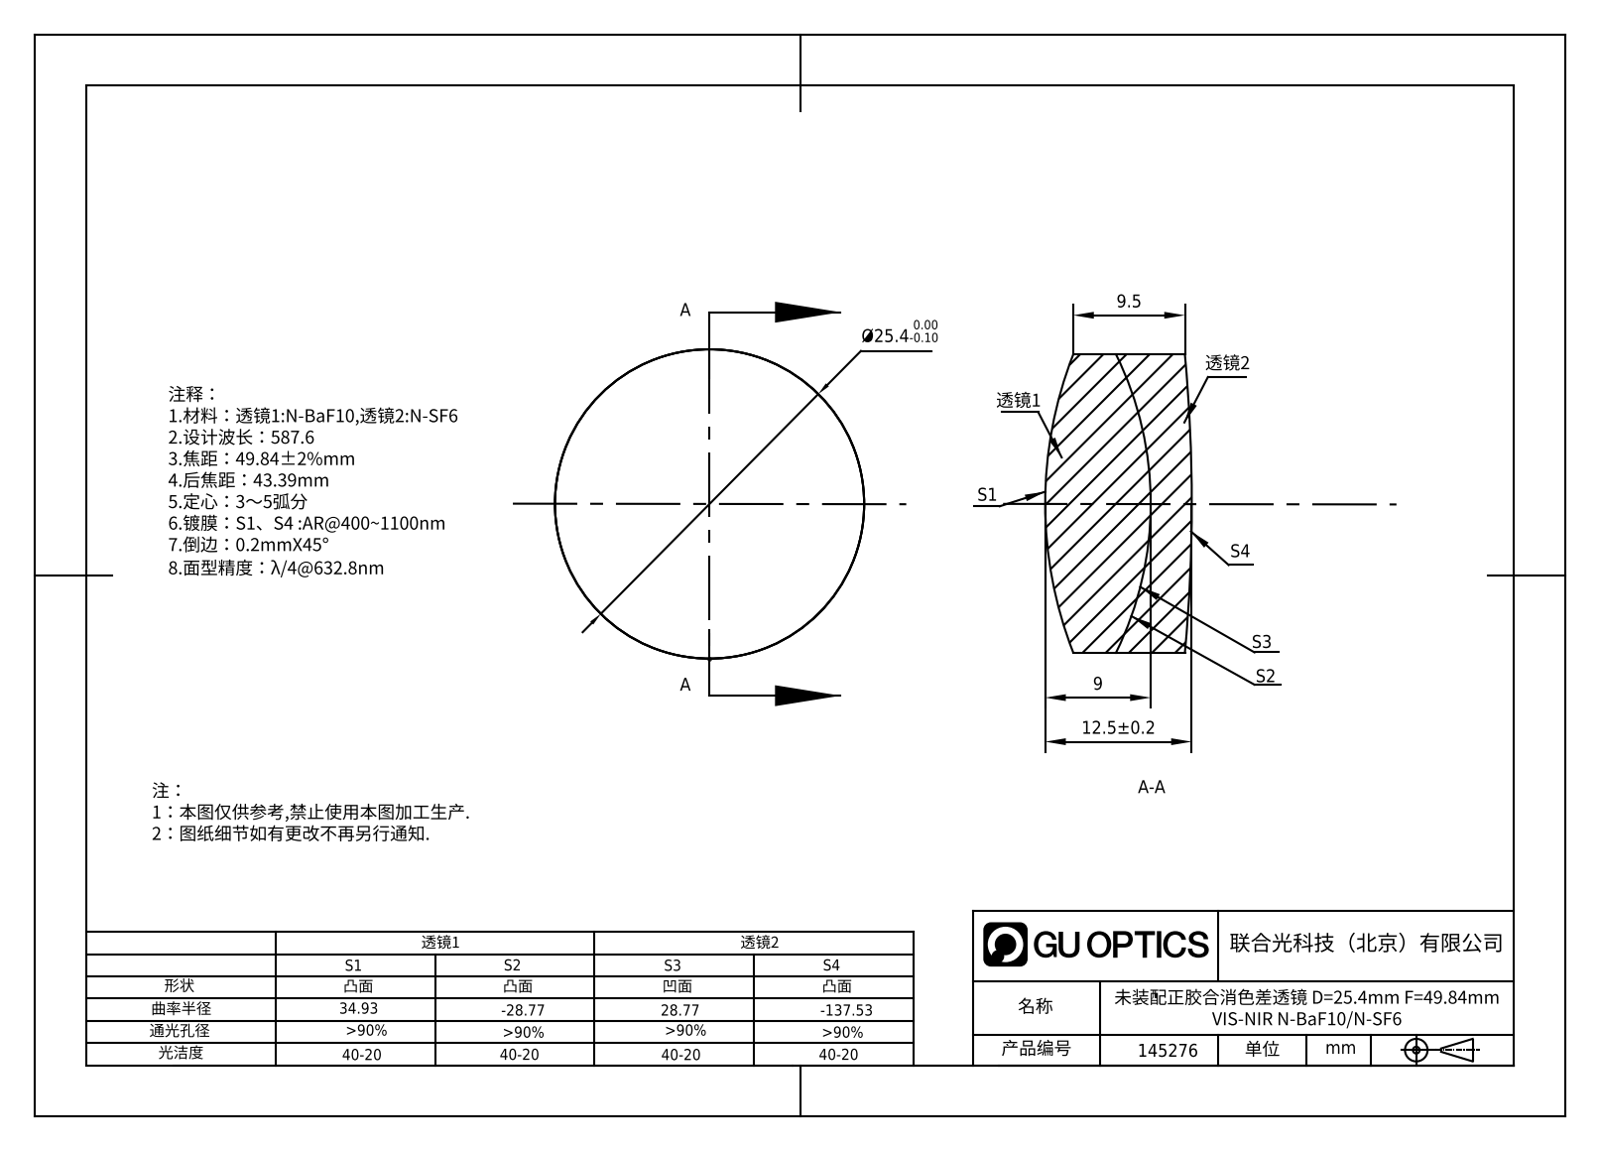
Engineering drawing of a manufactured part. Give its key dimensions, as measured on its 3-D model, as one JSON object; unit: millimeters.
{"part_name": "145276", "step_written_by": "SolidWorks 2020 (CONFIG_CONTROL_DESIGN)", "units": "millimeters", "bodies": {"solids": 2, "faces": 12, "planar": 0, "cylindrical": 4, "other": 8}, "overall_size": [25.4, 25.4, 12.5], "volume_mm3": 5587, "surface_area_mm2": 2861, "round_bosses_or_shafts": [[25.4, 1]]}
